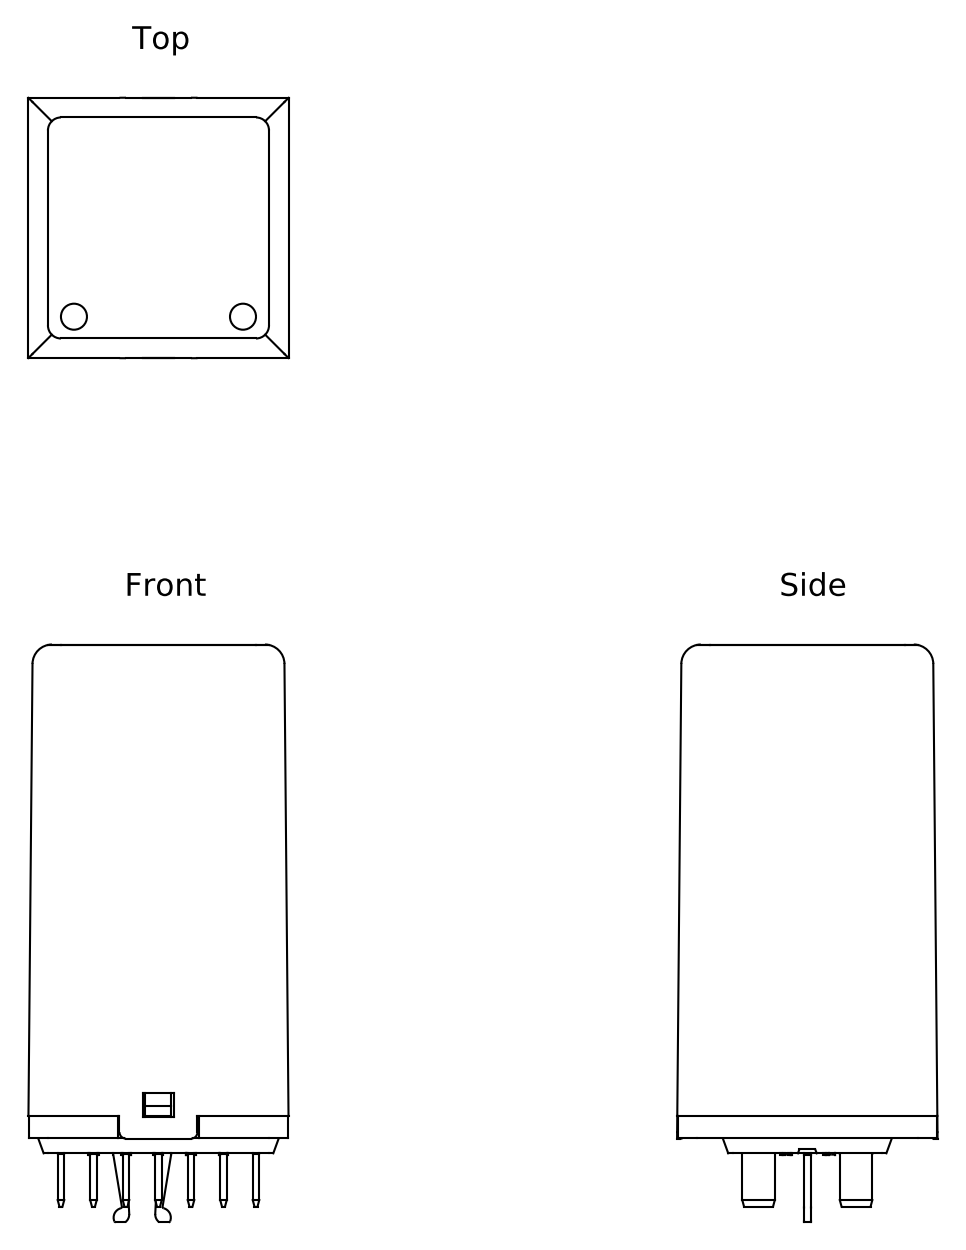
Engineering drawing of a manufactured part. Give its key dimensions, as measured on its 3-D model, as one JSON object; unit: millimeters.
{"part_name": "TDBE-U200", "step_written_by": "Autodesk Inventor 2011 (AUTOMOTIVE_DESIGN)", "units": "millimeters", "bodies": {"solids": 1, "faces": 1487, "planar": 899, "cylindrical": 409, "other": 179}, "overall_size": [88.85, 40.06, 40], "volume_mm3": 29390, "surface_area_mm2": 35739, "round_holes": [[1.6, 2], [2.7, 2], [4, 2], [4.1, 2], [4.6, 2], [1.7, 1]], "round_bosses_or_shafts": [[2.7, 1]], "partial_cylinders_radius": [[0.2, 74], [0.28, 56], [1.5, 24], [1, 8], [2, 8], [3, 8], [0.5, 4], [0.6, 4]], "face_to_face_distances": [1.5, 5, 10, 15, 1, 20, 4, 6, 11, 9], "hole_center_spacings": [13.8, 26, 4, 27.61, 31.15, 8.5, 12.5, 13.5]}
